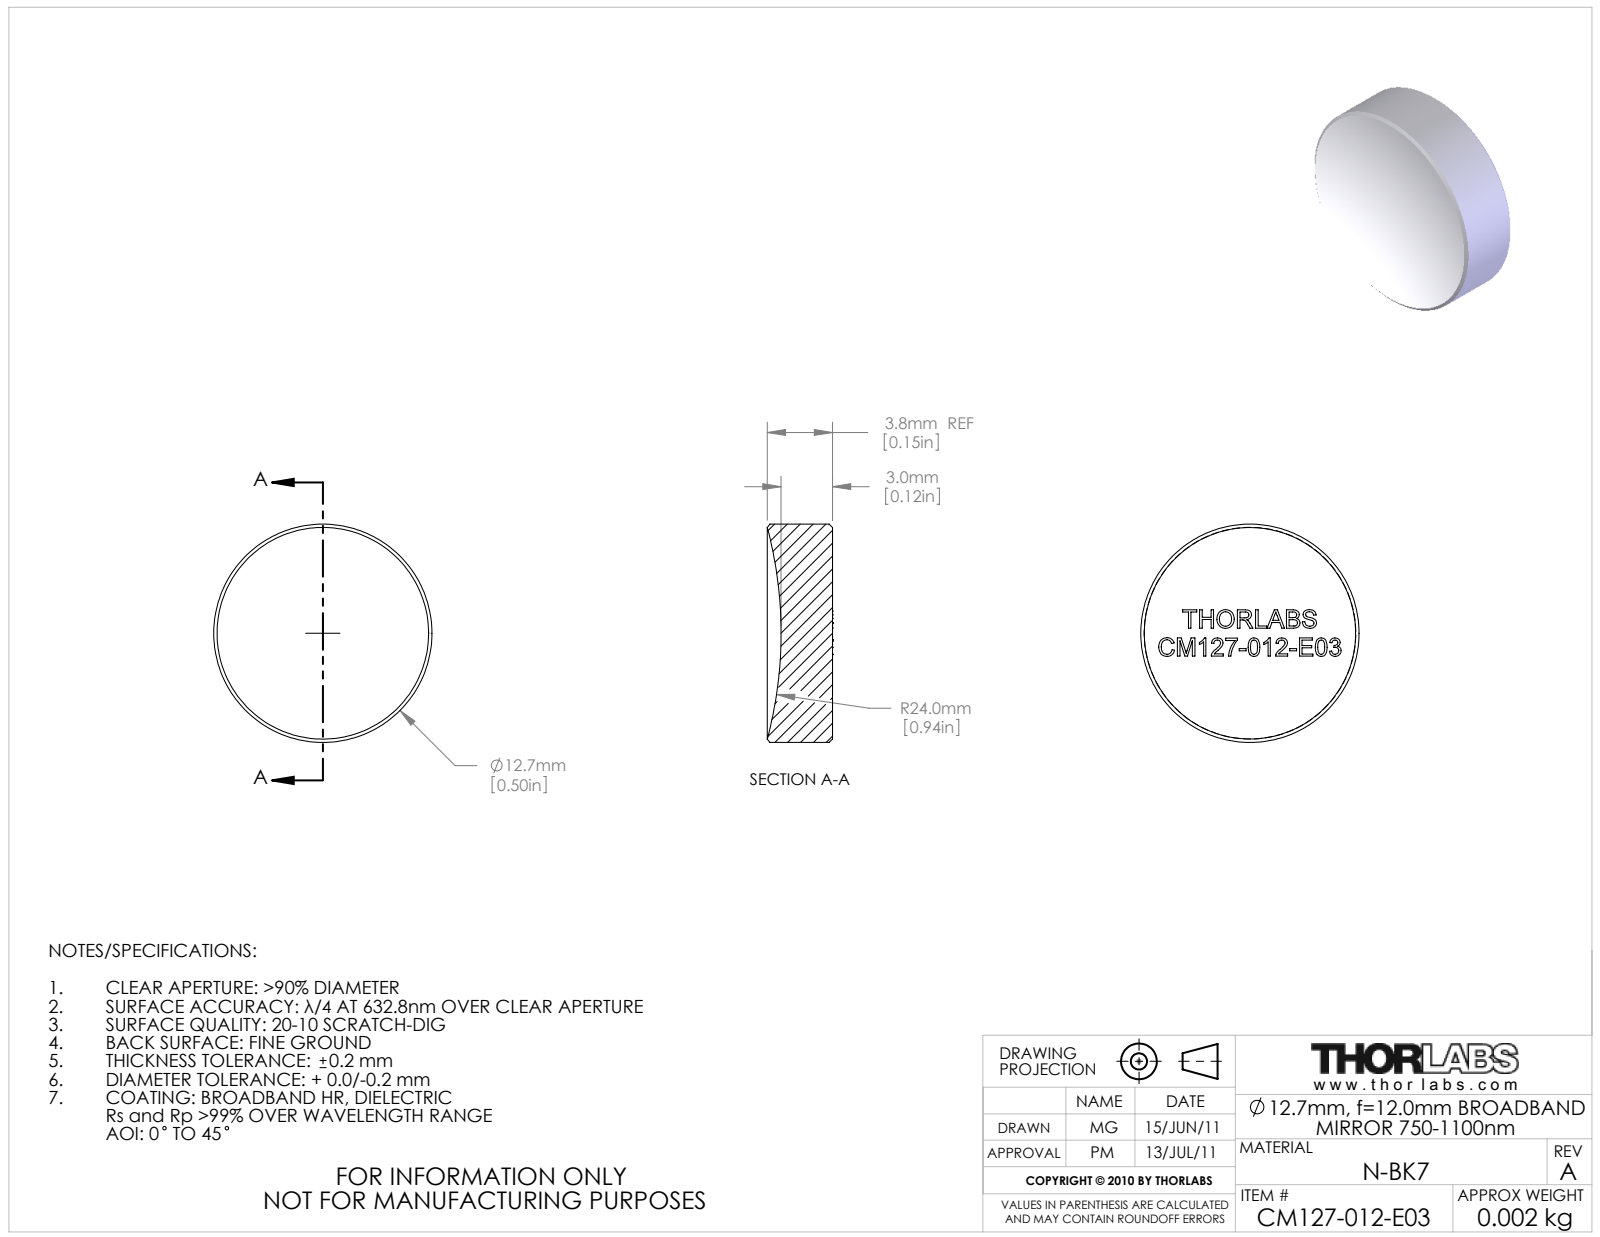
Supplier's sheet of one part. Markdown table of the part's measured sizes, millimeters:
| quantity | value |
| --- | --- |
| part name | 22638-E0W |
| STEP written by | SolidWorks 2011 (AUTOMOTIVE_DESIGN) |
| units | millimeters |
| bodies | 0 solids, 43 faces (33 planar, 2 cylindrical, 8 other) |
| overall size | 12.7 × 12.7 × 3.8 |
| round bosses / shafts (diameter × count) | 12.7 × 1 |
| main face-to-face distances | 2.08, 1.02, 1.06 |
